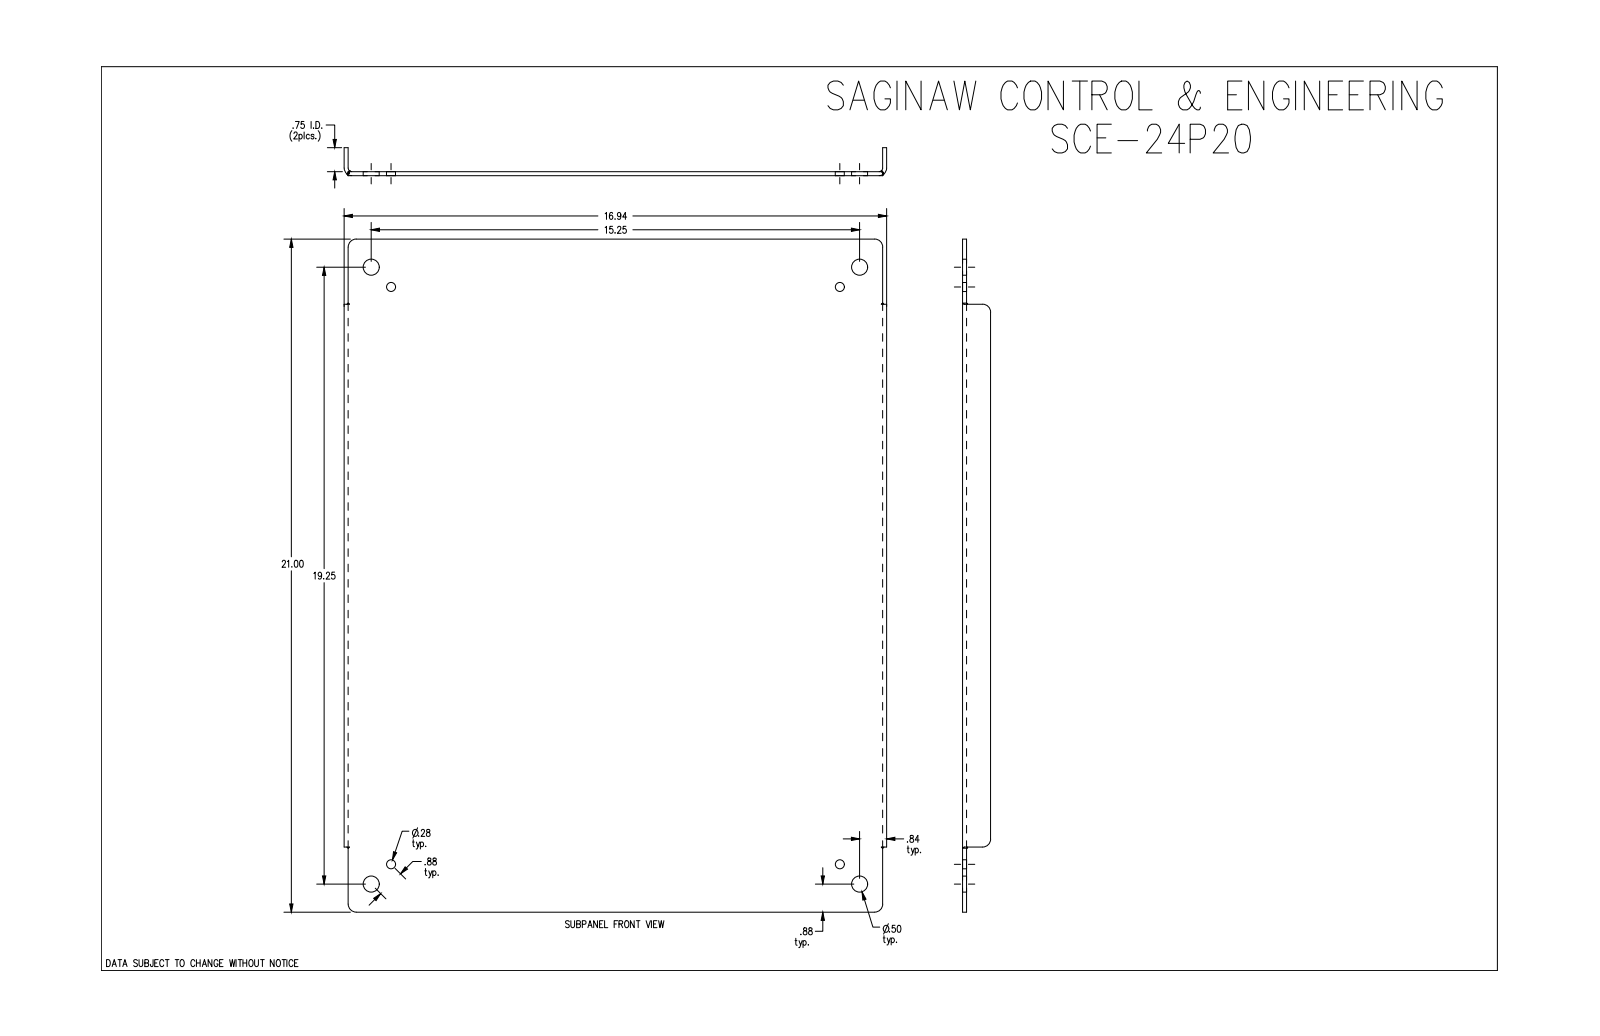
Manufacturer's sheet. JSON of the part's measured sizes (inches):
{"part_name": "SCE-24P20", "step_written_by": "SolidWorks 2019 (CONFIG_CONTROL_DESIGN)", "units": "inches", "bodies": {"solids": 1, "faces": 50, "planar": 18, "cylindrical": 20, "other": 12}, "overall_size": [21, 16.938, 0.875], "volume_in3": 47.05, "surface_area_in2": 763.7, "round_holes": [[0.281, 4], [0.5, 4]], "partial_cylinders_radius": [[0.25, 6], [0.112, 2], [0.237, 2]], "face_to_face_distances": [0.125, 0.125, 16.813, 16.687, 16.938, 0.75, 0.875, 21, 2.031, 18.969], "hole_center_spacings": [0.875, 14.644, 18.641, 23.689, 14.013, 15.25, 18.013, 19.25]}
